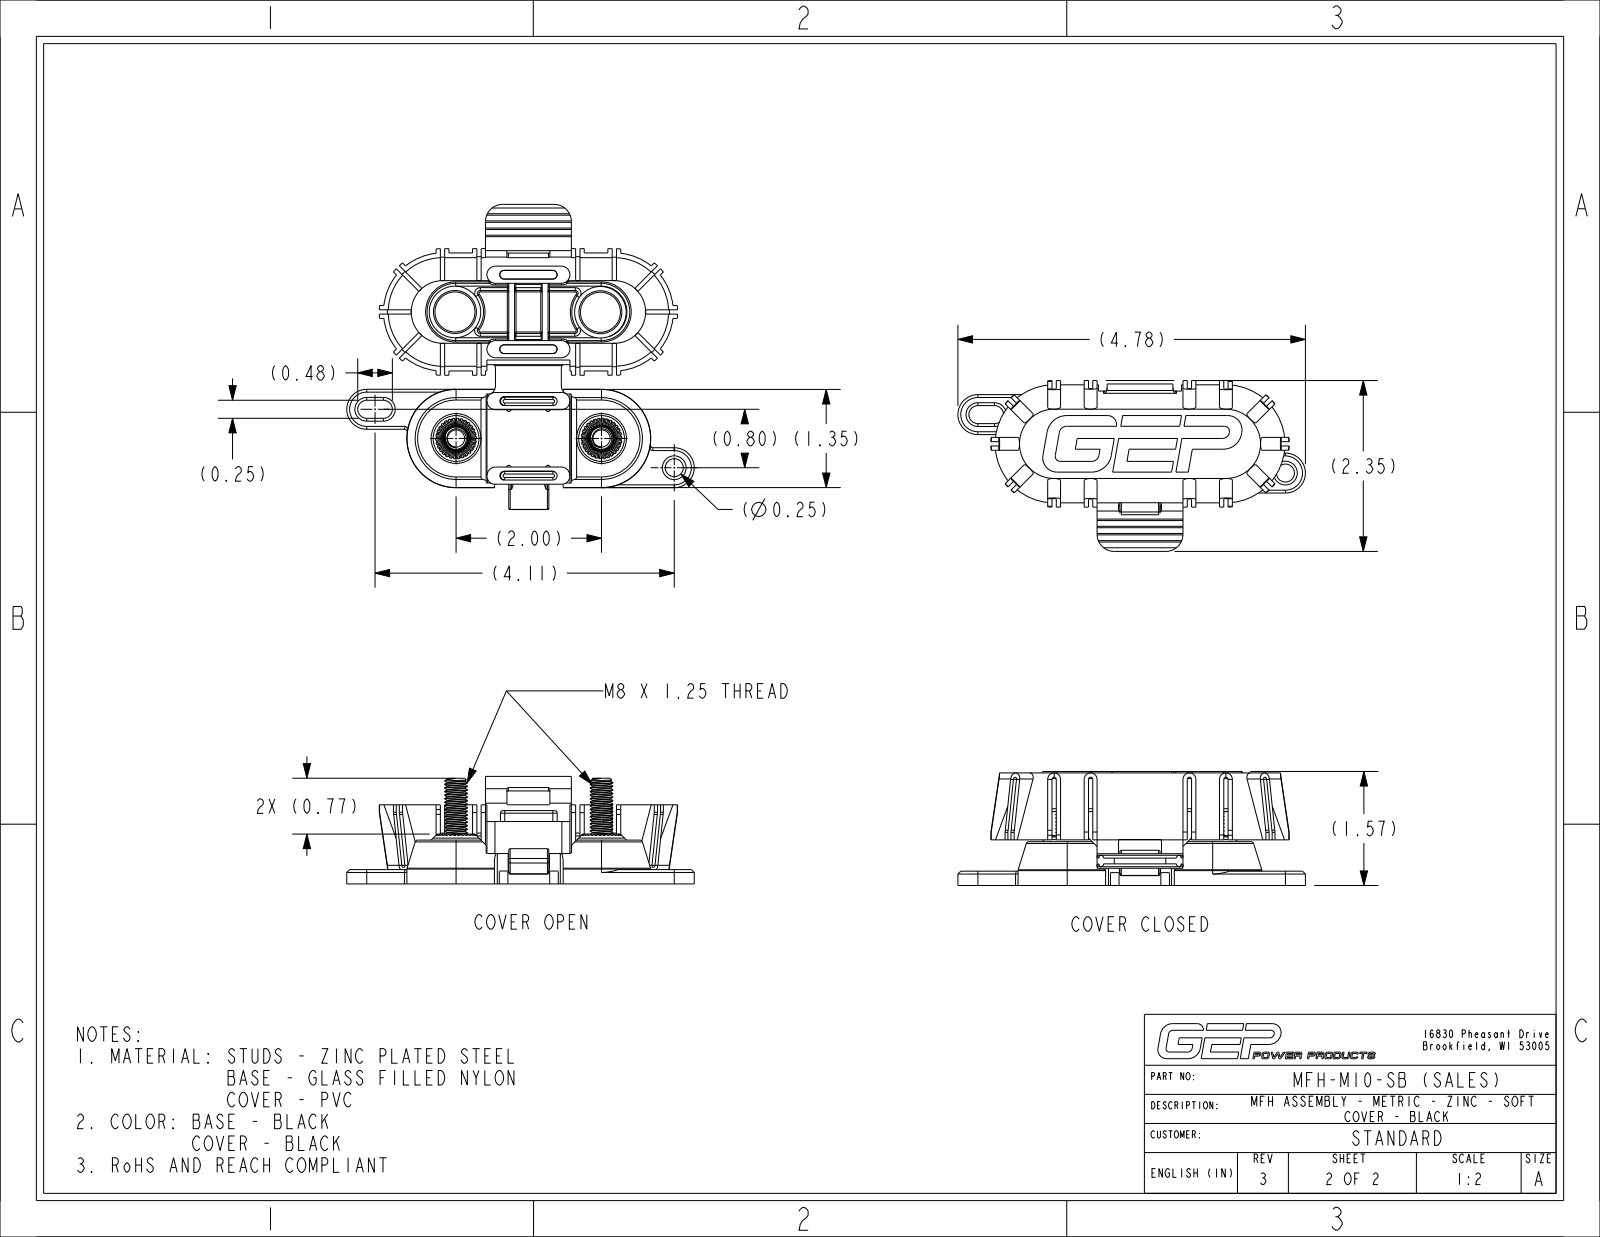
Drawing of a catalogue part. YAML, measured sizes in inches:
part_name: "MFH-MXX-XX_BODY_NCF; C05-1003-M1_NCF; MFH-SB_NCF_INSTALLED; MFH-M10-SB_INSTALLED_NCF_ASM"
step_written_by: "CREO PARAMETRIC BY PTC INC, 2024014 (CONFIG_CONTROL_DESIGN)"
units: inches
bodies: {solids: 4, faces: 2099, planar: 769, cylindrical: 729, other: 601}
overall_size: [4.778, 2.348, 1.567]
volume: 3.169
surface_area: 83.8
round_holes:
  - {diameter: 0.354, count: 2}
  - {diameter: 0.591, count: 2}
  - {diameter: 0.248, count: 1}
round_bosses_or_shafts:
  - {diameter: 0.63, count: 2}
  - {diameter: 0.315, count: 2}
partial_cylinders:
  - {radius: 0.016, count: 236}
  - {radius: 0.02, count: 24}
  - {radius: 0.039, count: 20}
  - {radius: 0.02, count: 14}
  - {radius: 0.015, count: 13}
  - {radius: 0.012, count: 10}
  - {radius: 0.035, count: 10}
  - {radius: 0.059, count: 10}
face_to_face_distances: [0.059, 0.118, 0.079, 0.423, 0.177, 0.945, 1.024, 1.13, 0.02, 0.6]
hole_center_spacings: [2, 1.078, 1.087, 1.991, 2.009, 3.027, 3.036]
